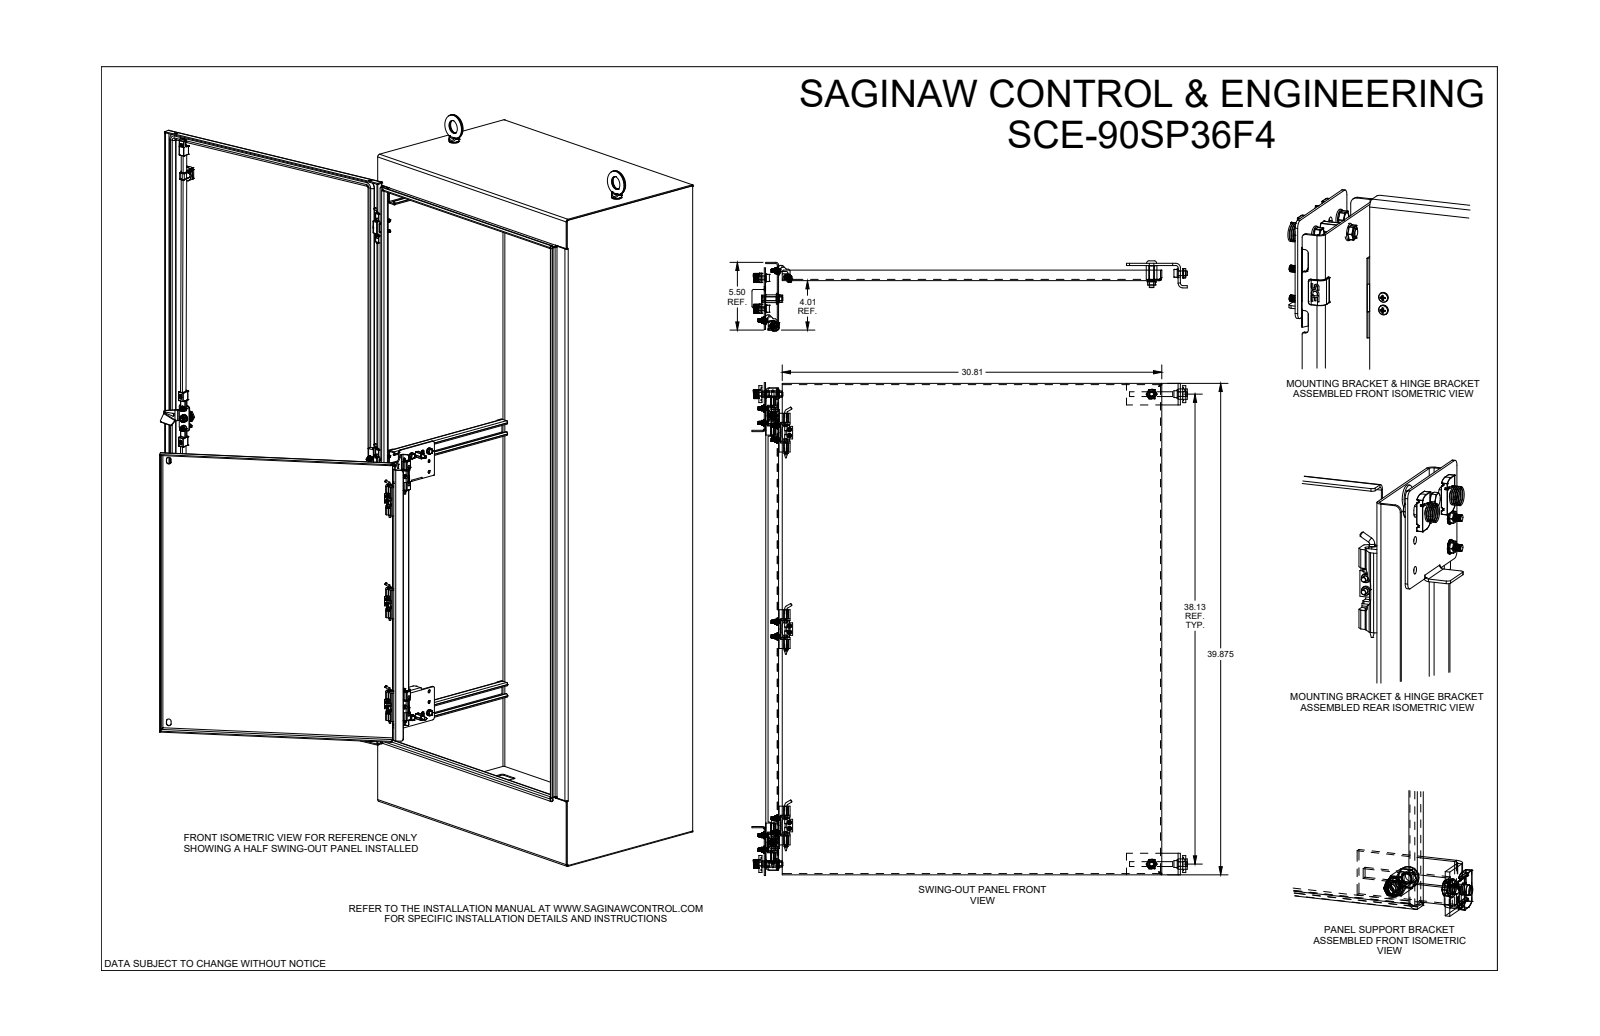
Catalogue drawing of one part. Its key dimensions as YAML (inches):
part_name: "SCE-90SP36F4"
step_written_by: "SolidWorks 2021 (AUTOMOTIVE_DESIGN)"
units: inches
bodies: {solids: 39, faces: 1855, planar: 892, cylindrical: 705, other: 258}
overall_size: [39.994, 35.336, 5.671]
volume: 180.5
surface_area: 3445
round_holes:
  - {diameter: 0.25, count: 16}
  - {diameter: 0.281, count: 14}
  - {diameter: 0.36, count: 10}
  - {diameter: 0.218, count: 8}
  - {diameter: 0.19, count: 6}
  - {diameter: 0.04, count: 5}
  - {diameter: 0.156, count: 2}
  - {diameter: 0.201, count: 2}
  - {diameter: 0.33, count: 2}
  - {diameter: 0.375, count: 2}
  - {diameter: 0.383, count: 2}
  - {diameter: 0.204, count: 1}
round_bosses_or_shafts:
  - {diameter: 0.196, count: 7}
  - {diameter: 0.34, count: 6}
  - {diameter: 0.249, count: 6}
  - {diameter: 0.886, count: 2}
  - {diameter: 0.813, count: 2}
  - {diameter: 0.5, count: 2}
  - {diameter: 0.368, count: 2}
  - {diameter: 0.31, count: 2}
partial_cylinders:
  - {radius: 0.011, count: 36}
  - {radius: 0.015, count: 20}
  - {radius: 0.188, count: 16}
  - {radius: 0.25, count: 16}
  - {radius: 0.1, count: 14}
  - {radius: 0.06, count: 11}
  - {radius: 0.07, count: 11}
  - {radius: 0.025, count: 10}
face_to_face_distances: [0.104, 1.058, 1.385, 31.108, 32.166, 5.396, 4.011, 39.771, 0.954, 1.162]
hole_center_spacings: [0.592, 15.937, 1.181, 34.625, 31.875, 0.5, 2.098, 2.92]
